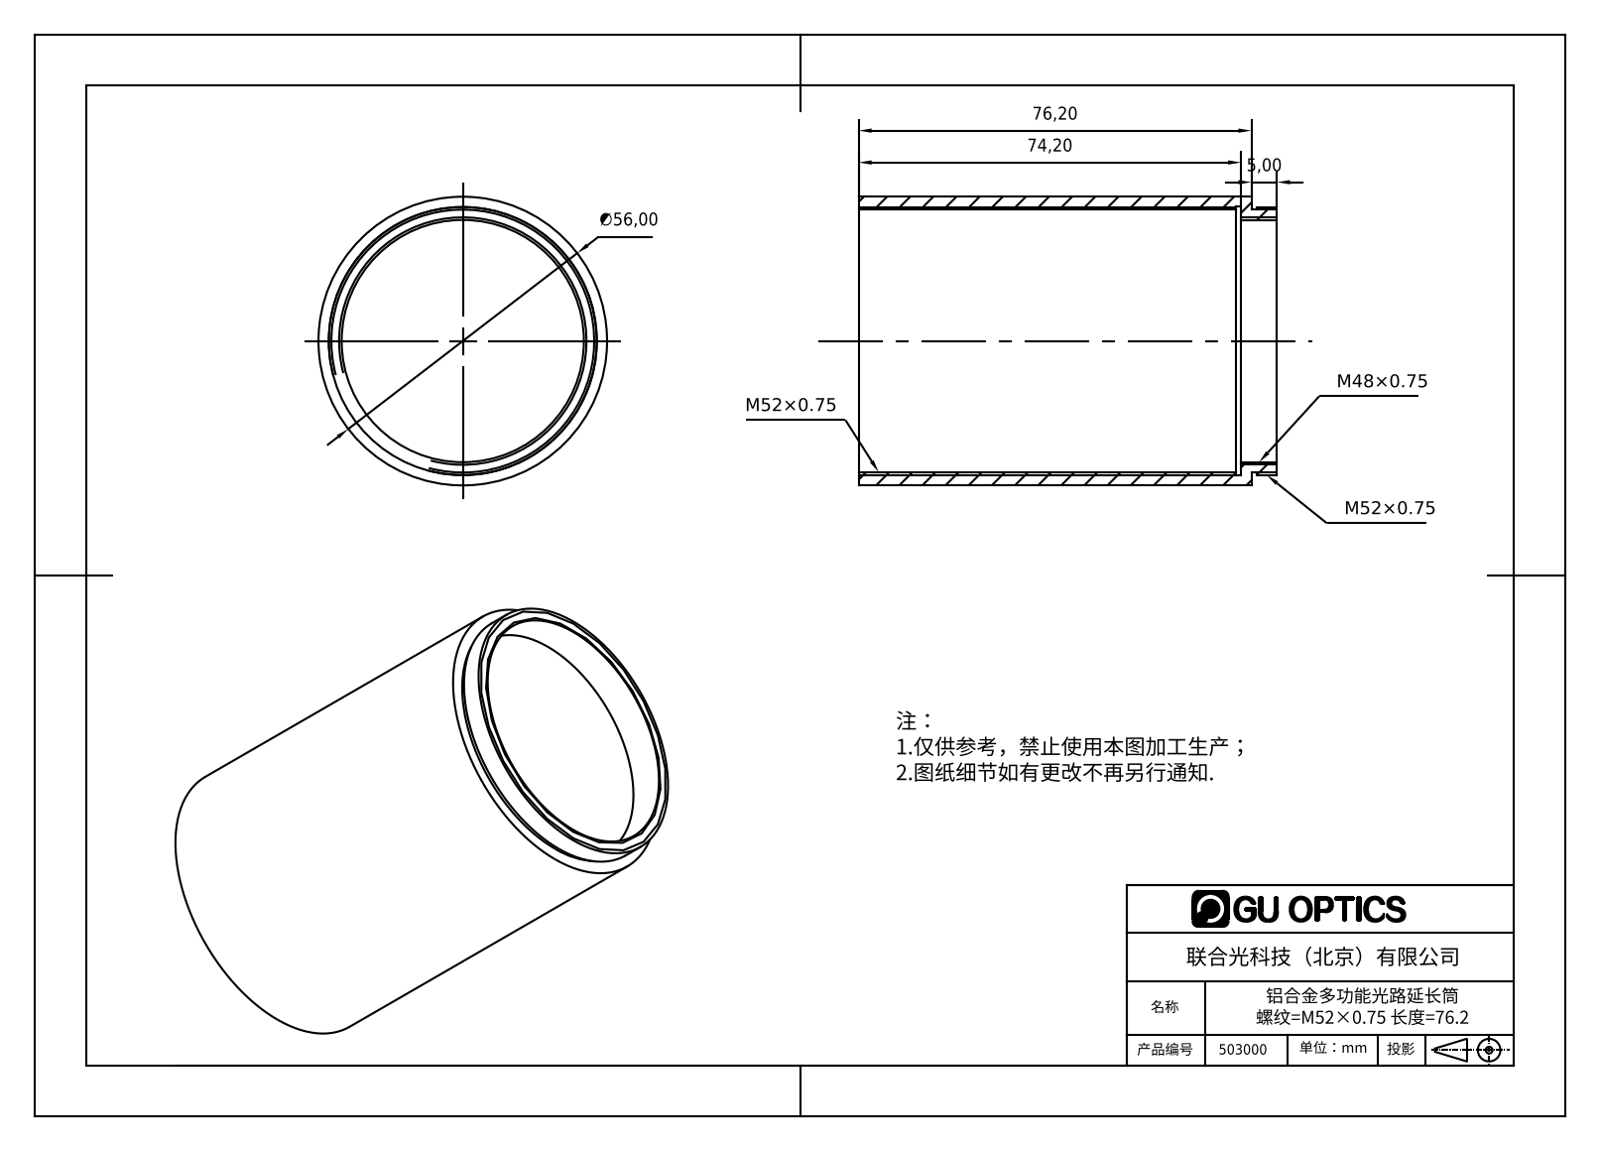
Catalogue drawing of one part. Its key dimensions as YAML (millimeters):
part_name: "503000"
step_written_by: "SolidWorks 2016 (AUTOMOTIVE_DESIGN)"
units: millimeters
bodies: {solids: 1, faces: 18, planar: 6, cylindrical: 12, other: 0}
overall_size: [81.2, 56, 56]
volume: 34400
surface_area: 28958
round_holes:
  - {diameter: 47, count: 1}
  - {diameter: 51, count: 1}
  - {diameter: 52.2, count: 1}
round_bosses_or_shafts:
  - {diameter: 56, count: 1}
  - {diameter: 52, count: 1}
face_to_face_distances: [76.2, 74.2, 2, 81.2, 7, 5, 1, 3, 4, 73.2]
